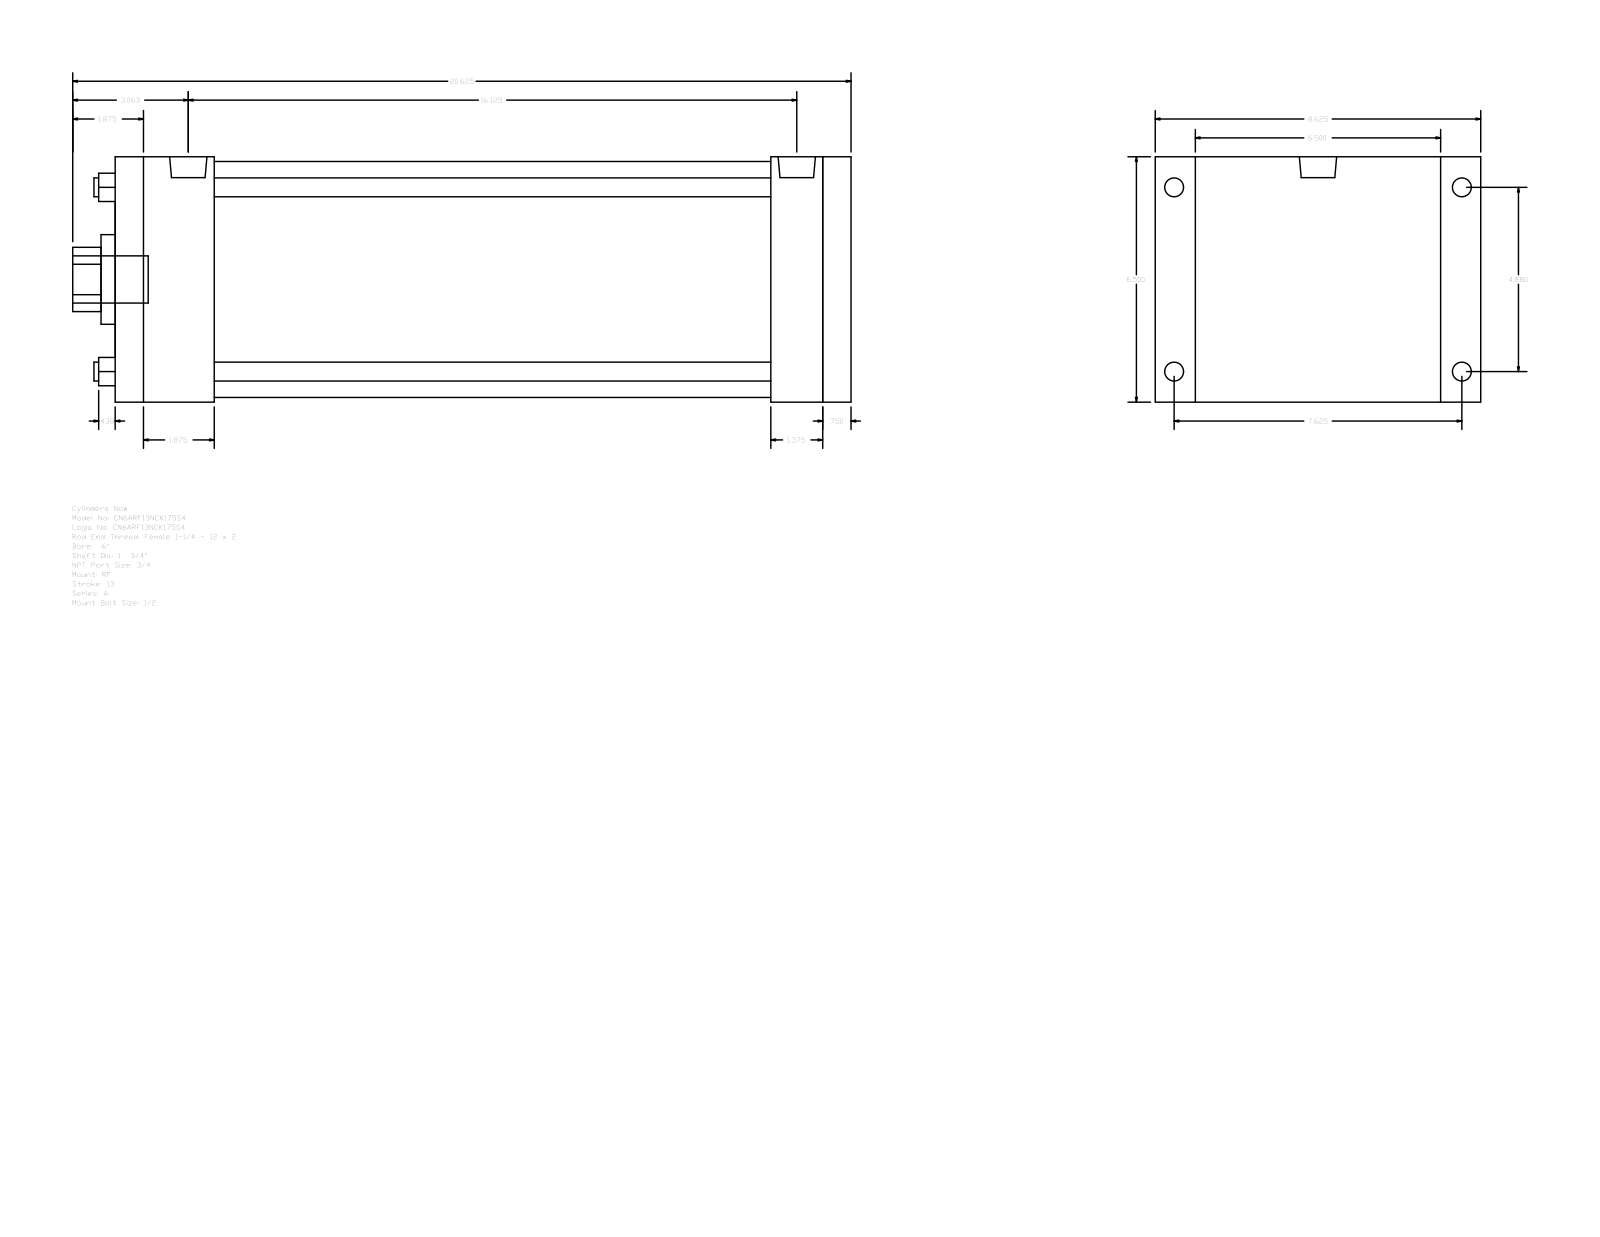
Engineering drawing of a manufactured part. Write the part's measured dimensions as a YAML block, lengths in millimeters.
part_name: "A_RF__0600_1.75"
step_written_by: "GSSL Pune (CONFIG_CONTROL_DESIGN)"
units: millimeters
bodies: {solids: 0, faces: 92, planar: 64, cylindrical: 28, other: 0}
overall_size: [523.88, 219.07, 165.1]
round_holes:
  - {diameter: 12.7, count: 4}
  - {diameter: 44.45, count: 1}
  - {diameter: 60.33, count: 1}
  - {diameter: 158.75, count: 1}
round_bosses_or_shafts:
  - {diameter: 15.08, count: 4}
  - {diameter: 12.7, count: 4}
  - {diameter: 25.12, count: 2}
  - {diameter: 31.75, count: 1}
partial_cylinders:
  - {radius: 21.63, count: 1}
face_to_face_distances: [165.1, 495.31, 476.25, 19.06, 34.92, 66.68, 409.57, 428.63, 441.33, 374.65]
hole_center_spacings: [87.65, 123.96, 175.31]
